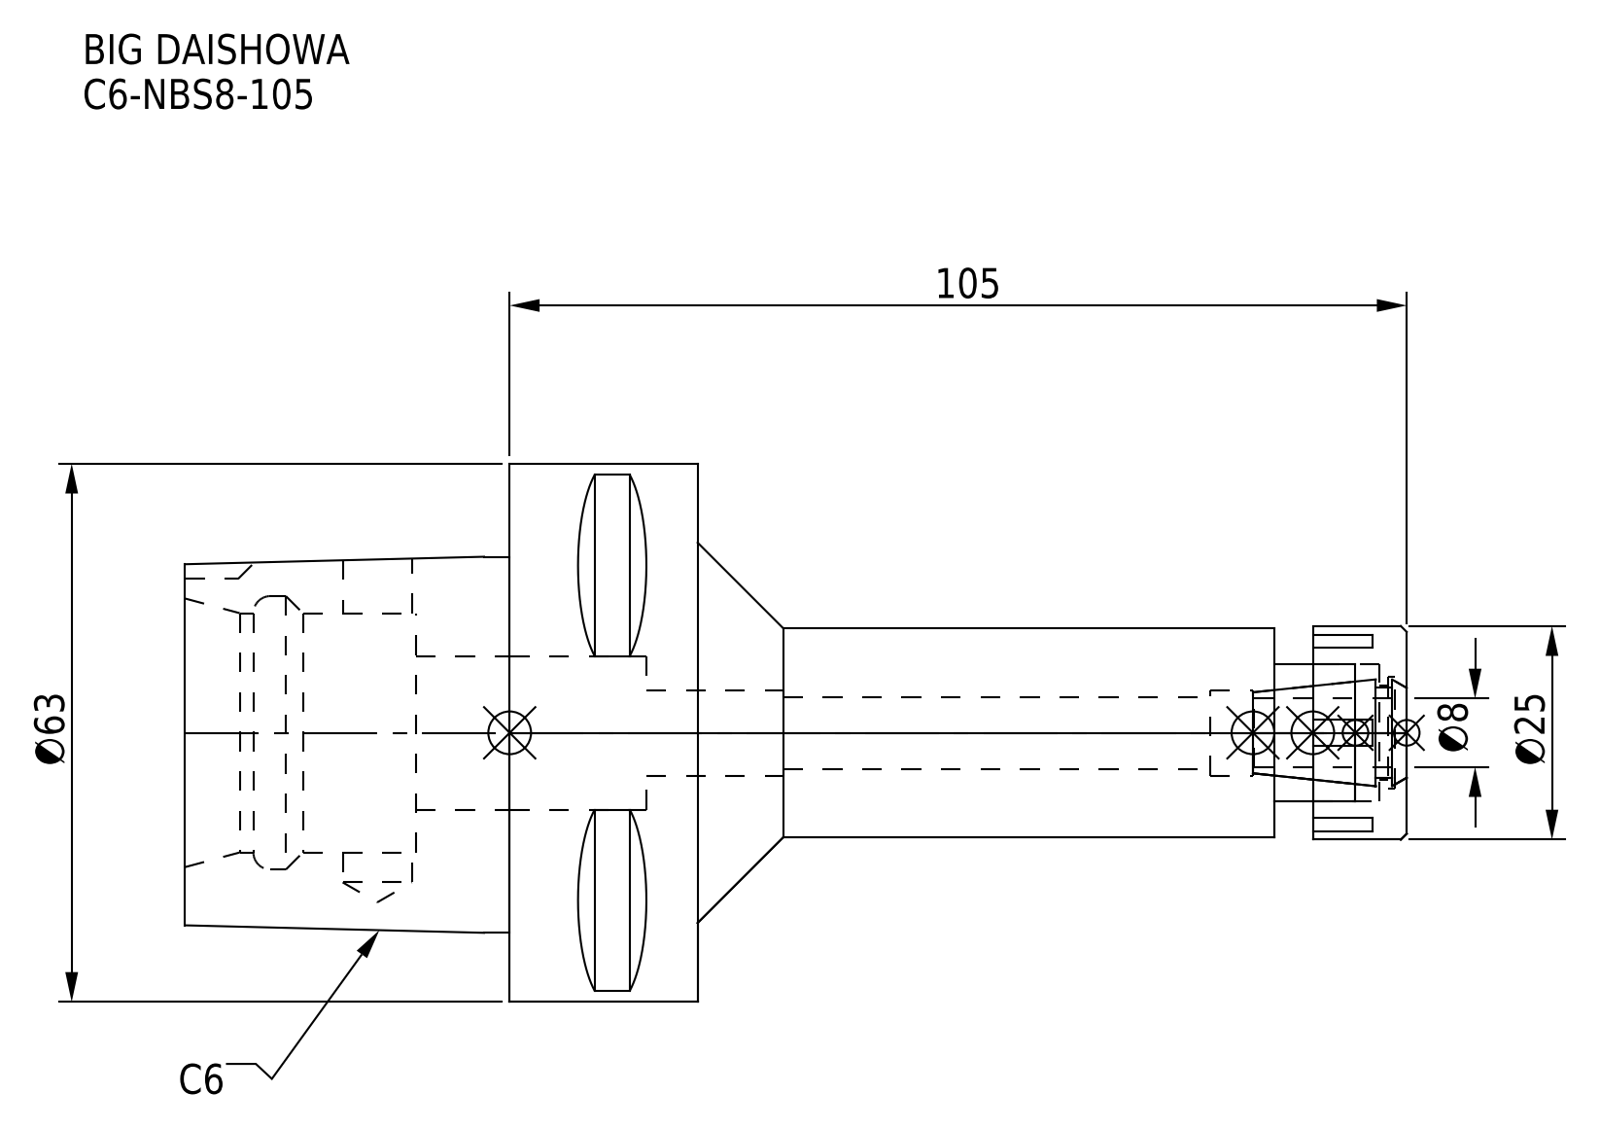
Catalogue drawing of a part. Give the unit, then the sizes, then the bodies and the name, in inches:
Units: inches
Overall size (bounding box): 5.63 × 2.48 × 2.48
Round holes (diameter × count): ⌀0.319 ×1, ⌀0.331 ×1, ⌀0.394 ×1, ⌀0.433 ×1, ⌀0.512 ×1, ⌀0.63 ×1, ⌀0.709 ×1, ⌀1.102 ×1, ⌀1.26 ×1
Round bosses / shafts (diameter × count): ⌀2.48 ×1, ⌀0.984 ×1, ⌀0.965 ×1
Partial cylindrical surfaces — rounded edges, fillets, slot ends (radius × count): R0.197 ×1
Main face-to-face distances: 0.866, 0.433, 4.134, 1.063, 2.362, 1.496, 3.268, 1.299, 4.567, 5.63
Volume: 8.115 in³ · Surface area: 46.6 in²
Bodies: 2 solids, 112 faces (61 planar, 33 cylindrical, 18 other)
Part name (STEP PRODUCT): C6-NBS8-105_1.stp; DXF_TEMP_ASSY_ASM_4_ASM.stp; C6-NBS8-105-080_ASM.stp; NBN8_1.stp (+3 more)
STEP written by: SolidWorks 2019 (CONFIG_CONTROL_DESIGN)
